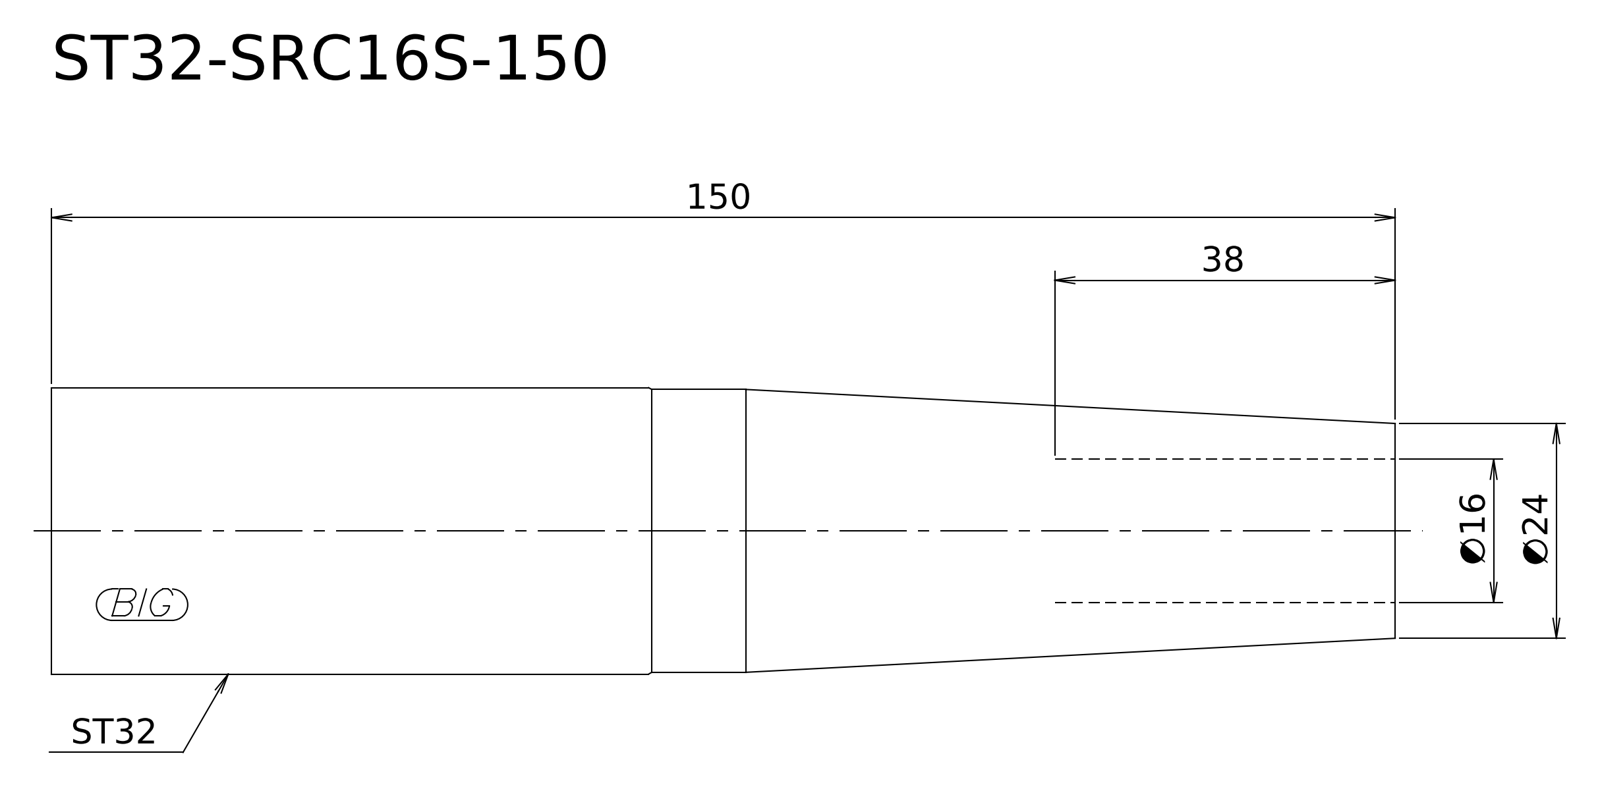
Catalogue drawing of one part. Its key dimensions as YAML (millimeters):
step_written_by: "Kubotek KeyCreator V8.5.1 (14335) (CONFIG_CONTROL_DESIGN)"
units: millimeters
bodies: {solids: 1, faces: 6, planar: 2, cylindrical: 2, other: 2}
overall_size: [150, 32, 32]
volume: 106395
surface_area: 15380
round_bosses_or_shafts:
  - {diameter: 32, count: 1}
  - {diameter: 31.6, count: 1}
face_to_face_distances: [150]
